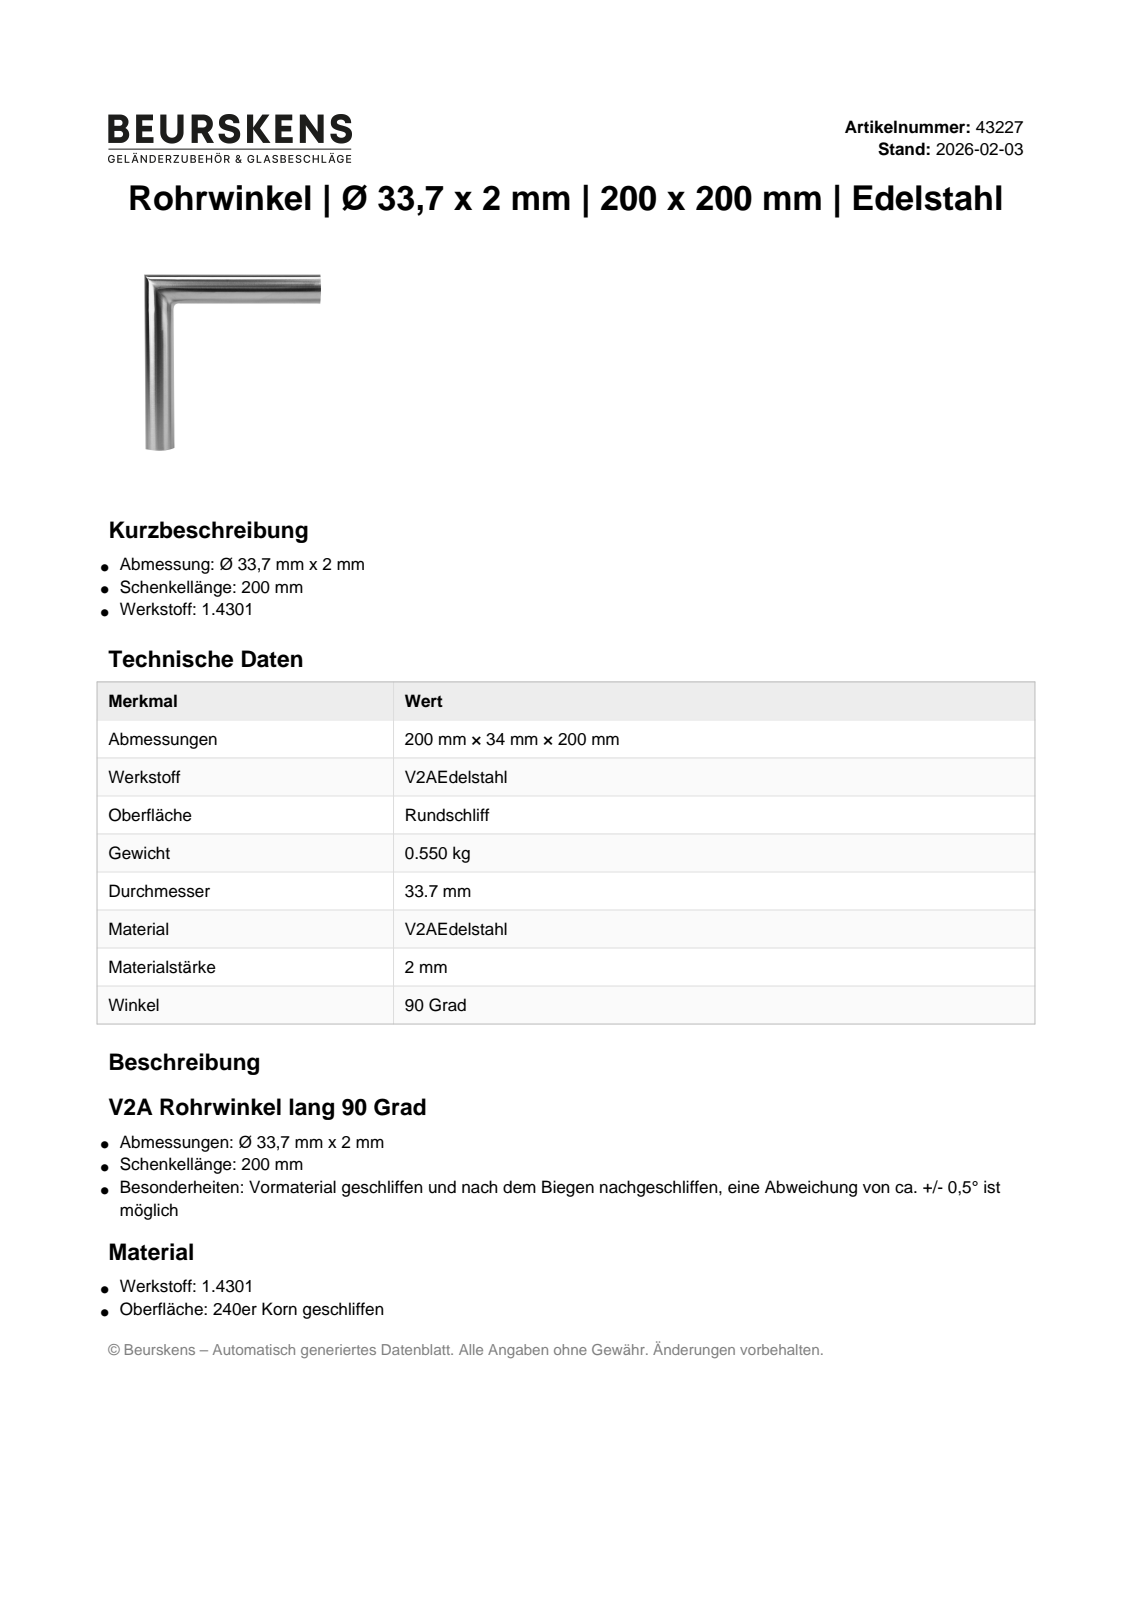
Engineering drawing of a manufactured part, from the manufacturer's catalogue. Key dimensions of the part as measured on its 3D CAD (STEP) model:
Part name (STEP PRODUCT): 43227
STEP written by: Autodesk Inventor 2022 (AUTOMOTIVE_DESIGN)
Units: millimetres
Bodies: 1 solid, 6 faces (2 planar, 4 cylindrical, 0 other)
Overall size (bounding box): 216.85 × 216.85 × 33.7
Volume: 79 671 mm³ · Surface area: 80 069 mm²
Round holes (diameter × count): ⌀29.7 ×2
Round bosses / shafts (diameter × count): ⌀33.7 ×2
